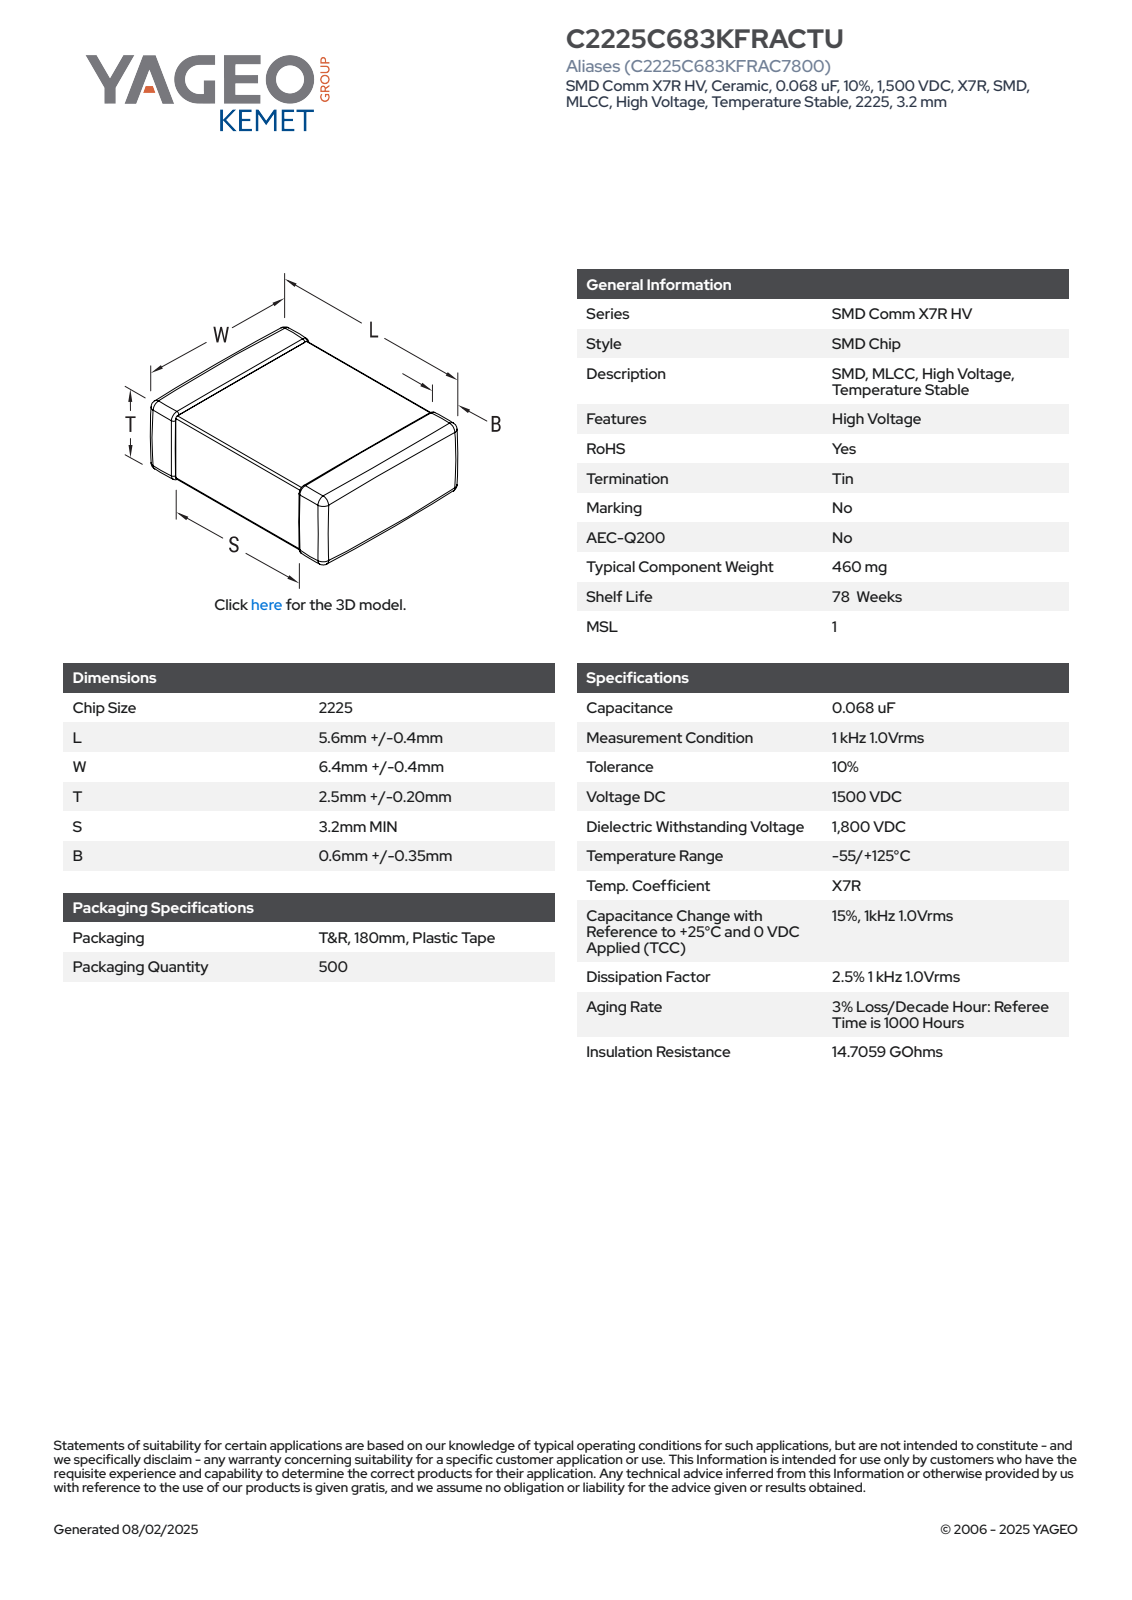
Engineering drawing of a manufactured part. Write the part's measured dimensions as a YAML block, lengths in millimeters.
part_name: "CCS_CCSTD_2225_L6W6.8T2.7B0.6"
step_written_by: "SolidWorks 2021 (AUTOMOTIVE_DESIGN)"
units: millimeters
bodies: {solids: 4, faces: 129, planar: 71, cylindrical: 42, other: 16}
overall_size: [6.8, 6, 2.7]
volume: 99
surface_area: 151
partial_cylinders:
  - {radius: 0.14, count: 24}
face_to_face_distances: [2.42, 2.56, 6, 6.52, 2.7, 6.66, 6.8, 1, 2.24, 3.76]
